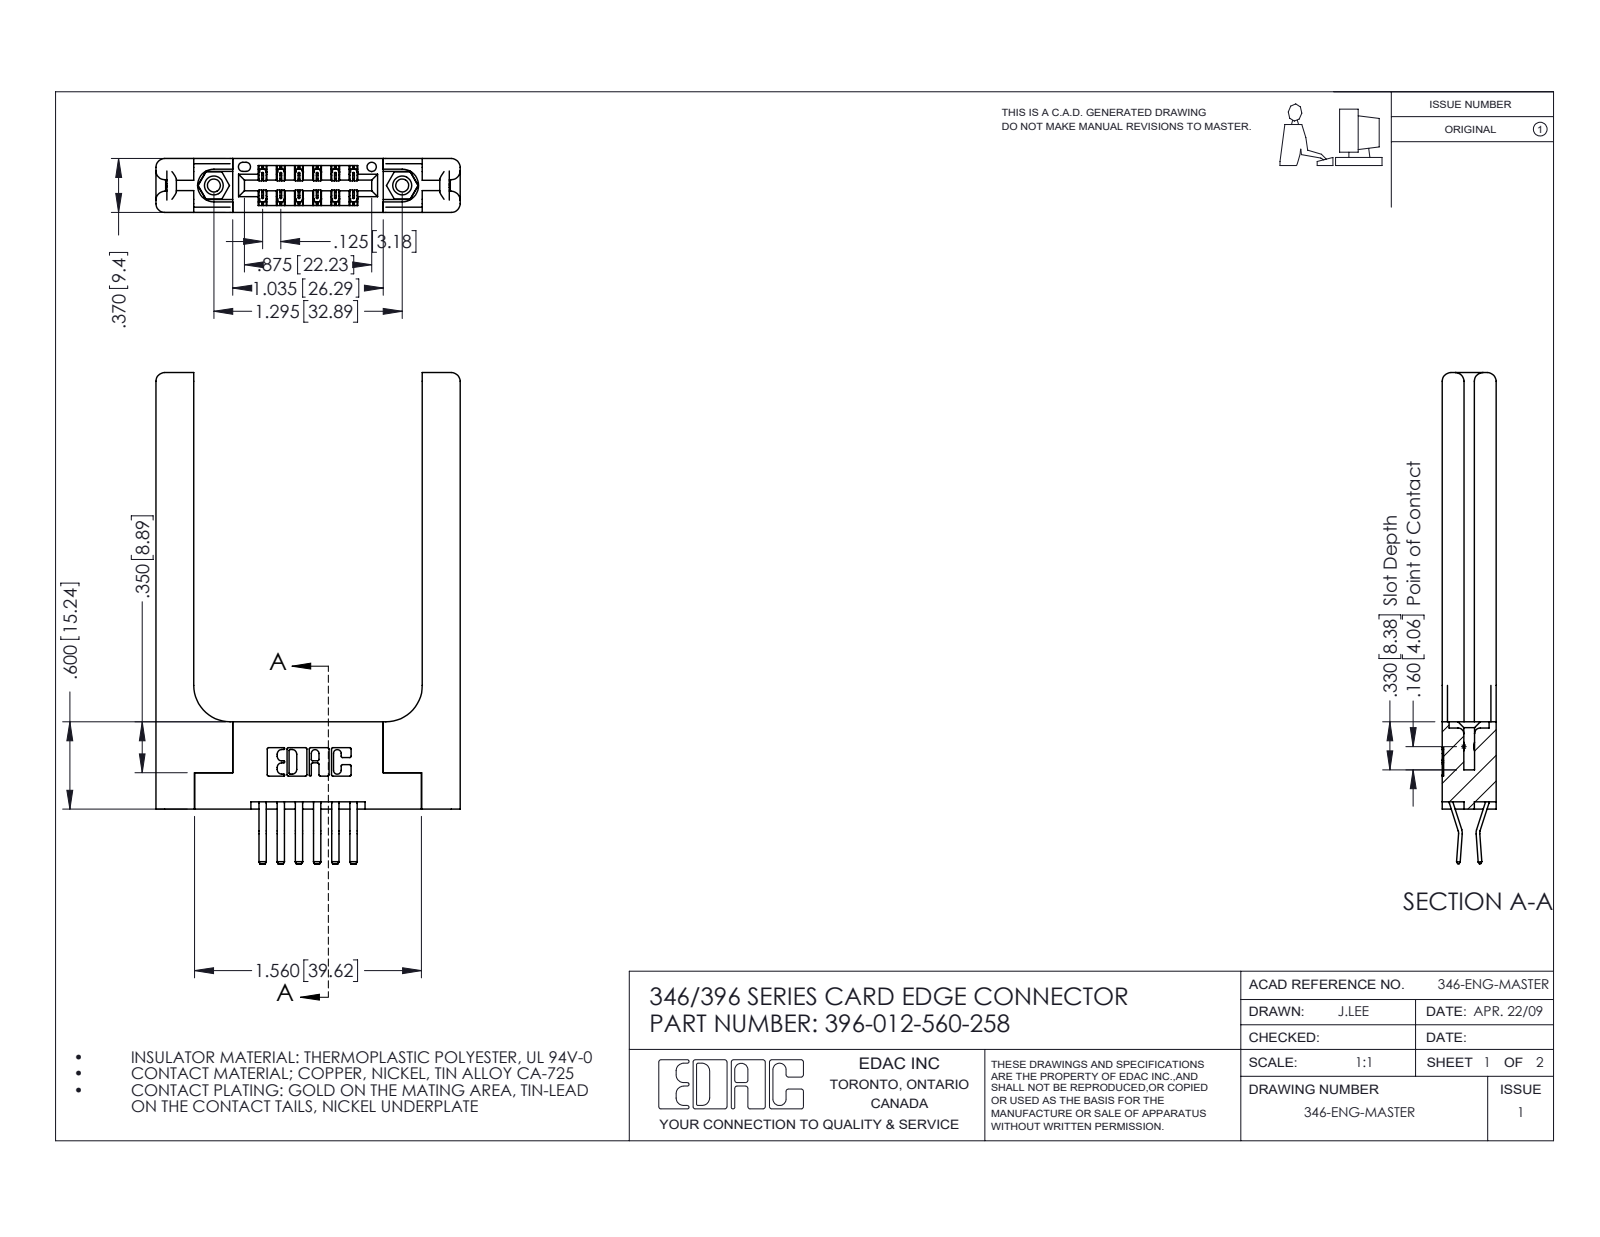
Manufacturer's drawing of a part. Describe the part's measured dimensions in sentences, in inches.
The part is named "345-292-001_560 Tail; 345-250-001_345-250-001-102; 346-220-058_345-220-058; 396-012-560-258 (+1 more)". Its 3-D file was written by "SolidWorks 2016 (CONFIG_CONTROL_DESIGN)". It is 17 solids with 1026 faces: 644 planar, 322 cylindrical and 60 other. Overall it measures 3.375 by 2.091 by 0.37 inches. Its volume is 0.761 cubic inches and its surface area 17.76 square inches. Round holes: 2 of diameter 0.089, 2 of diameter 0.125, 2 of diameter 0.156, 1 of diameter 0.064. Round bosses or shafts: 2 of diameter 0.155. Partial cylindrical surfaces (rounded edges, fillets, slot ends): 22 of radius 0.01, 18 of radius 0.006, 16 of radius 0.06, 6 of radius 0.007, 6 of radius 0.031, 3 of radius 0.026, 2 of radius 0.01, 2 of radius 0.014. The main face-to-face distances are 0.37, 0.15, 0.22, 0.25, 0.072, 0.148, 1.571, 0.102, 0.048, 0.322. The hole center spacings are 0.246, 1.092, 1.295.
